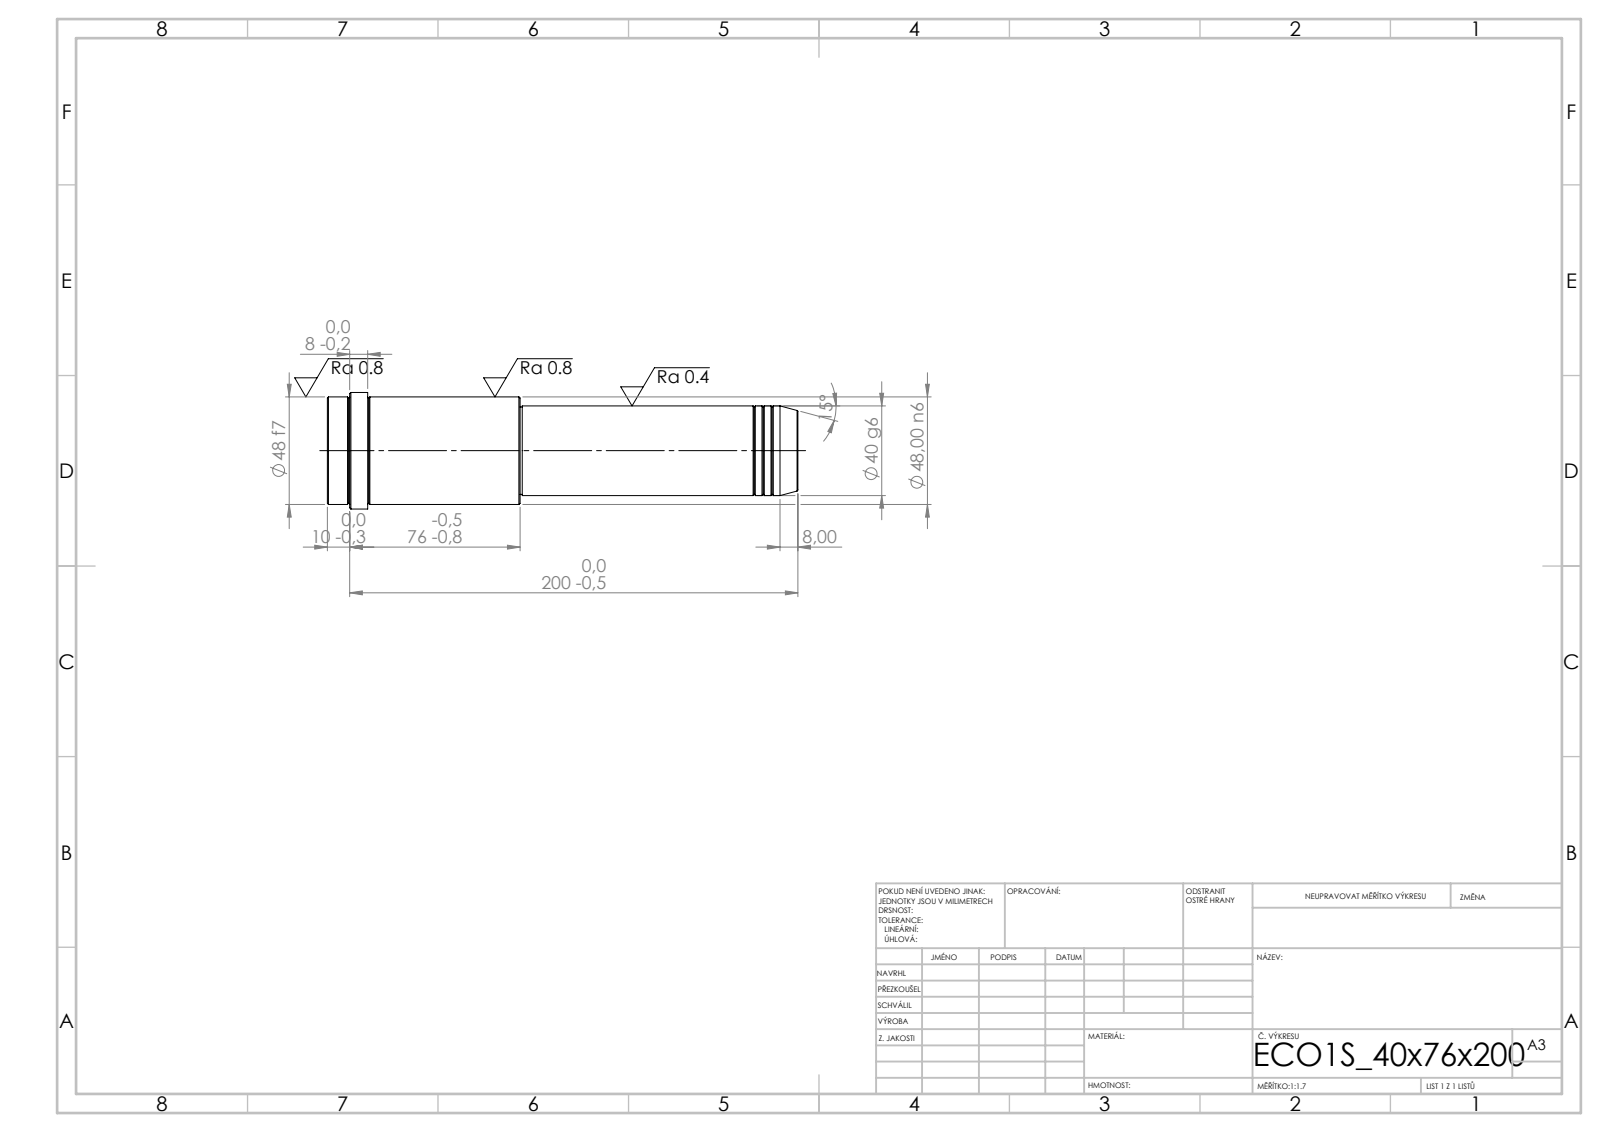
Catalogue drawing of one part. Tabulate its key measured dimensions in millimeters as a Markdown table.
| quantity | value |
| --- | --- |
| STEP written by | SolidWorks 2019 (CONFIG_CONTROL_DESIGN) |
| units | millimeters |
| bodies | 1 solid, 52 faces (6 planar, 16 cylindrical, 30 other) |
| overall size | 210 × 52 × 52 |
| volume | 312 532 mm³ |
| surface area | 32 966 mm² |
| round bosses / shafts (diameter × count) | 52 × 1, 48 × 1, 40 × 1, 39 × 1 |
| main face-to-face distances | 210, 124, 86, 192, 68, 18, 200, 76, 8, 10 |
